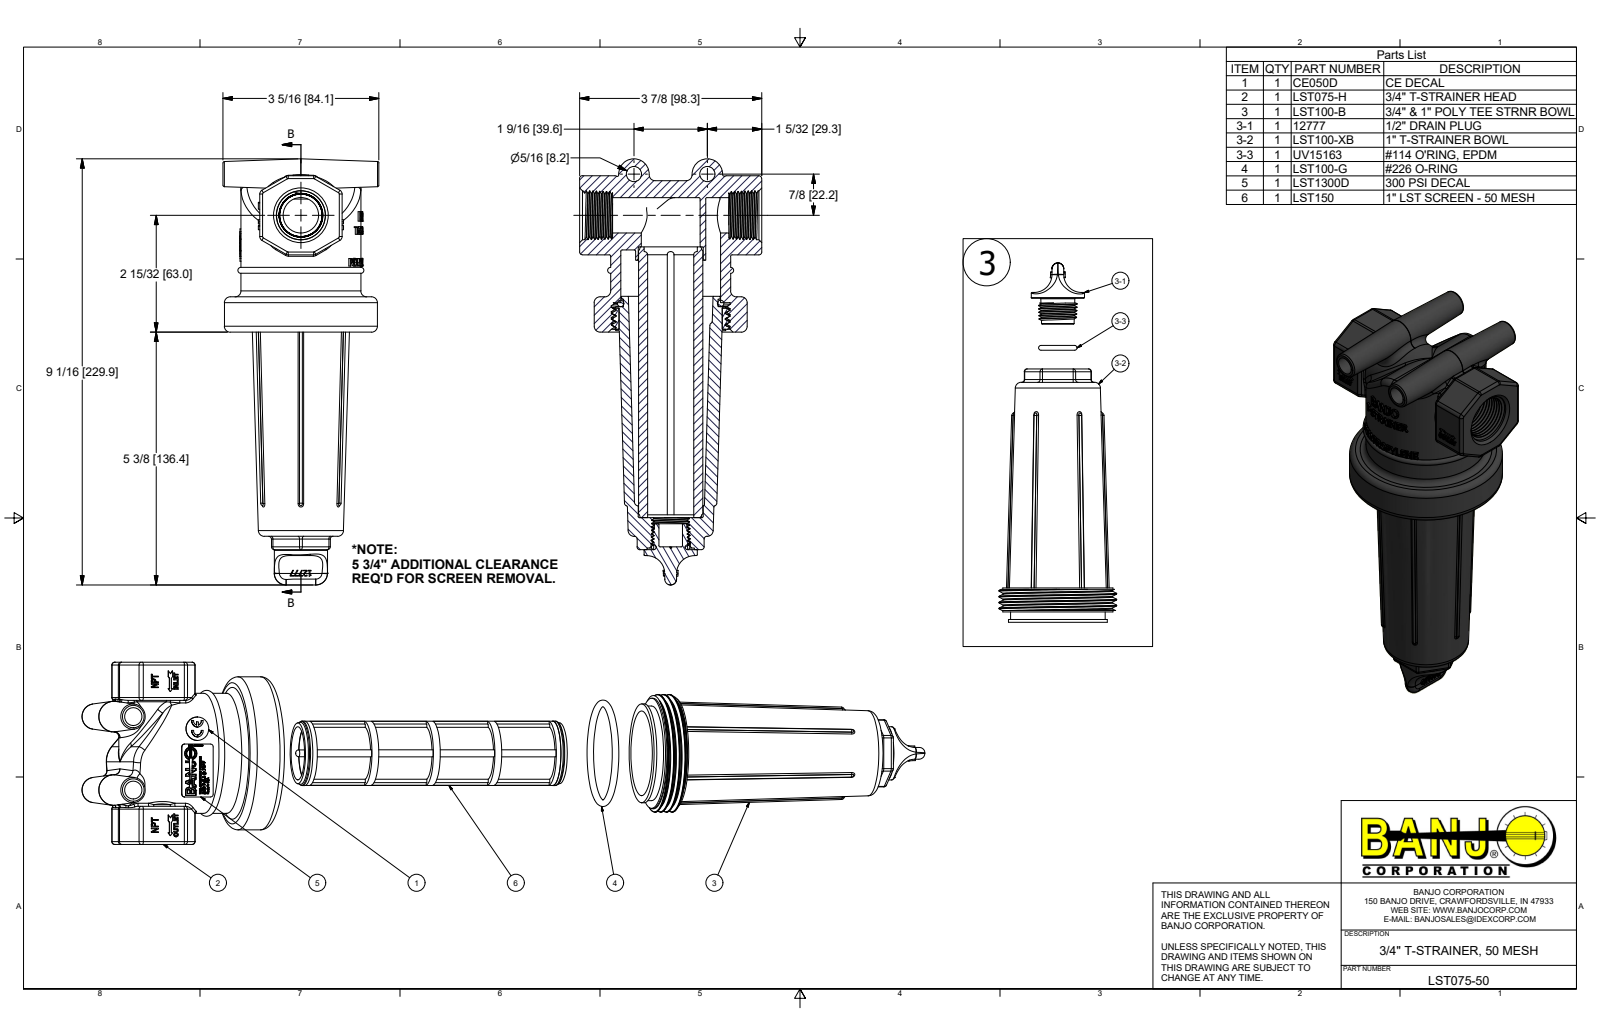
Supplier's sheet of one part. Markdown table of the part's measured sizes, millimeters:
| quantity | value |
| --- | --- |
| part name | LST075-50; CE050D; LST075-H; LST100-B (+6 more) |
| STEP written by | Autodesk Inventor 2018 (AUTOMOTIVE_DESIGN) |
| units | millimeters |
| bodies | 9 solids, 2844 faces (1569 planar, 258 cylindrical, 1017 other) |
| overall size | 361.9 × 98.3 × 84.1 |
| volume | 324 600 mm³ |
| surface area | 197 900 mm² |
| round holes (diameter × count) | 4.6 × 1, 6.5 × 1, 12.7 × 1, 19.1 × 1, 24.9 × 1, 25.5 × 1, 27.9 × 1, 31.8 × 1, 35.1 × 1, 53.8 × 1, 55.8 × 1, 60.9 × 1 |
| round bosses / shafts (diameter × count) | 82.6 × 1, 64.8 × 1, 63.5 × 1, 59.4 × 1, 53.3 × 1, 51.1 × 1, 37.8 × 1, 37.3 × 1 |
| partial cylindrical surfaces (radius × count) | 1.5 × 52, 0.8 × 11, 2.4 × 8, 1.9 × 4, 0.7 × 2, 0.8 × 2, 0.9 × 2, 1.6 × 2 |
| main face-to-face distances | 44.5, 6.4, 3.8, 19.1, 0.8, 13, 34.3, 26.7, 113, 30.5 |
